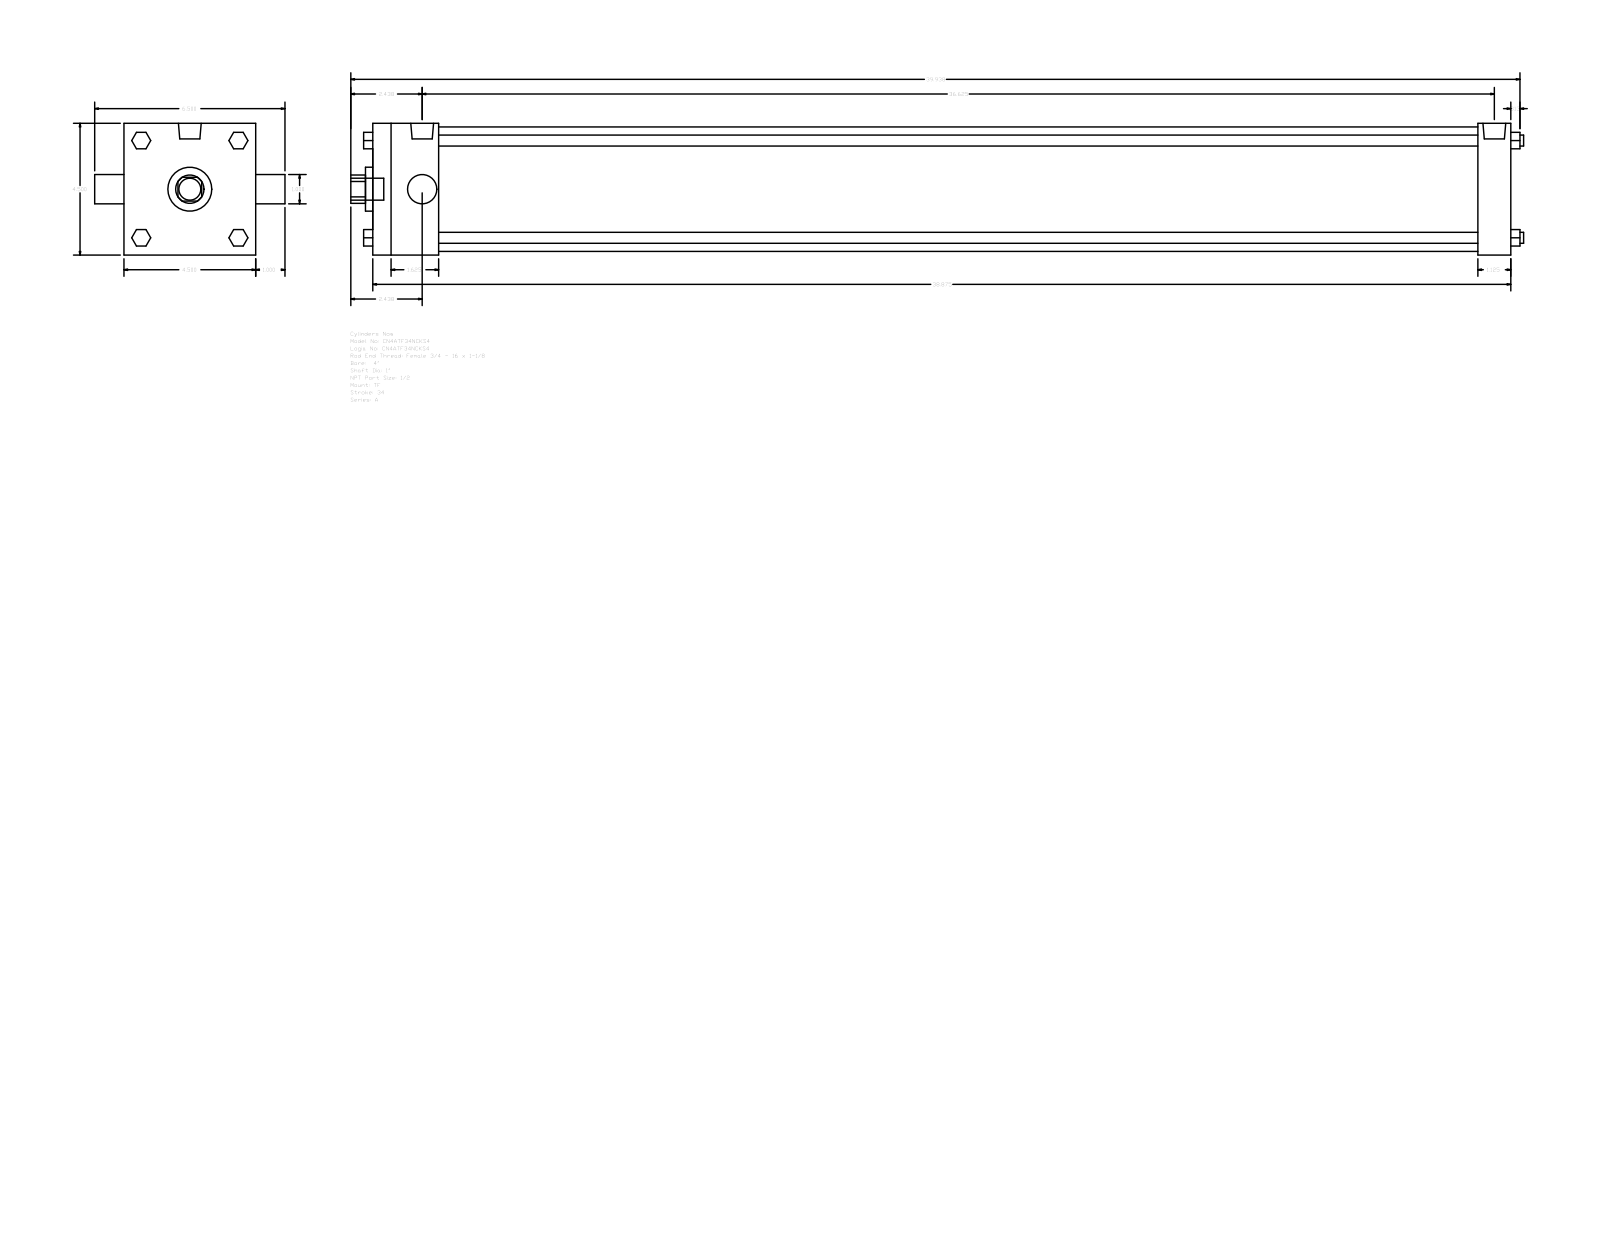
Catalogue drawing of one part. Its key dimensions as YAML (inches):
part_name: "A_TF__0400_1"
step_written_by: "GSSL Pune (CONFIG_CONTROL_DESIGN)"
units: inches
bodies: {solids: 0, faces: 120, planar: 92, cylindrical: 28, other: 0}
overall_size: [40.063, 6.5, 4.5]
round_holes:
  - {diameter: 1, count: 2}
  - {diameter: 1.5, count: 1}
  - {diameter: 4.25, count: 1}
round_bosses_or_shafts:
  - {diameter: 0.375, count: 4}
  - {diameter: 0.344, count: 3}
  - {diameter: 0.778, count: 2}
  - {diameter: 0.75, count: 1}
partial_cylinders:
  - {radius: 0.484, count: 1}
face_to_face_distances: [4.5, 38.875, 37.75, 1.125, 2.25, 35.5, 36.625, 0.563, 1.66, 2.875]
